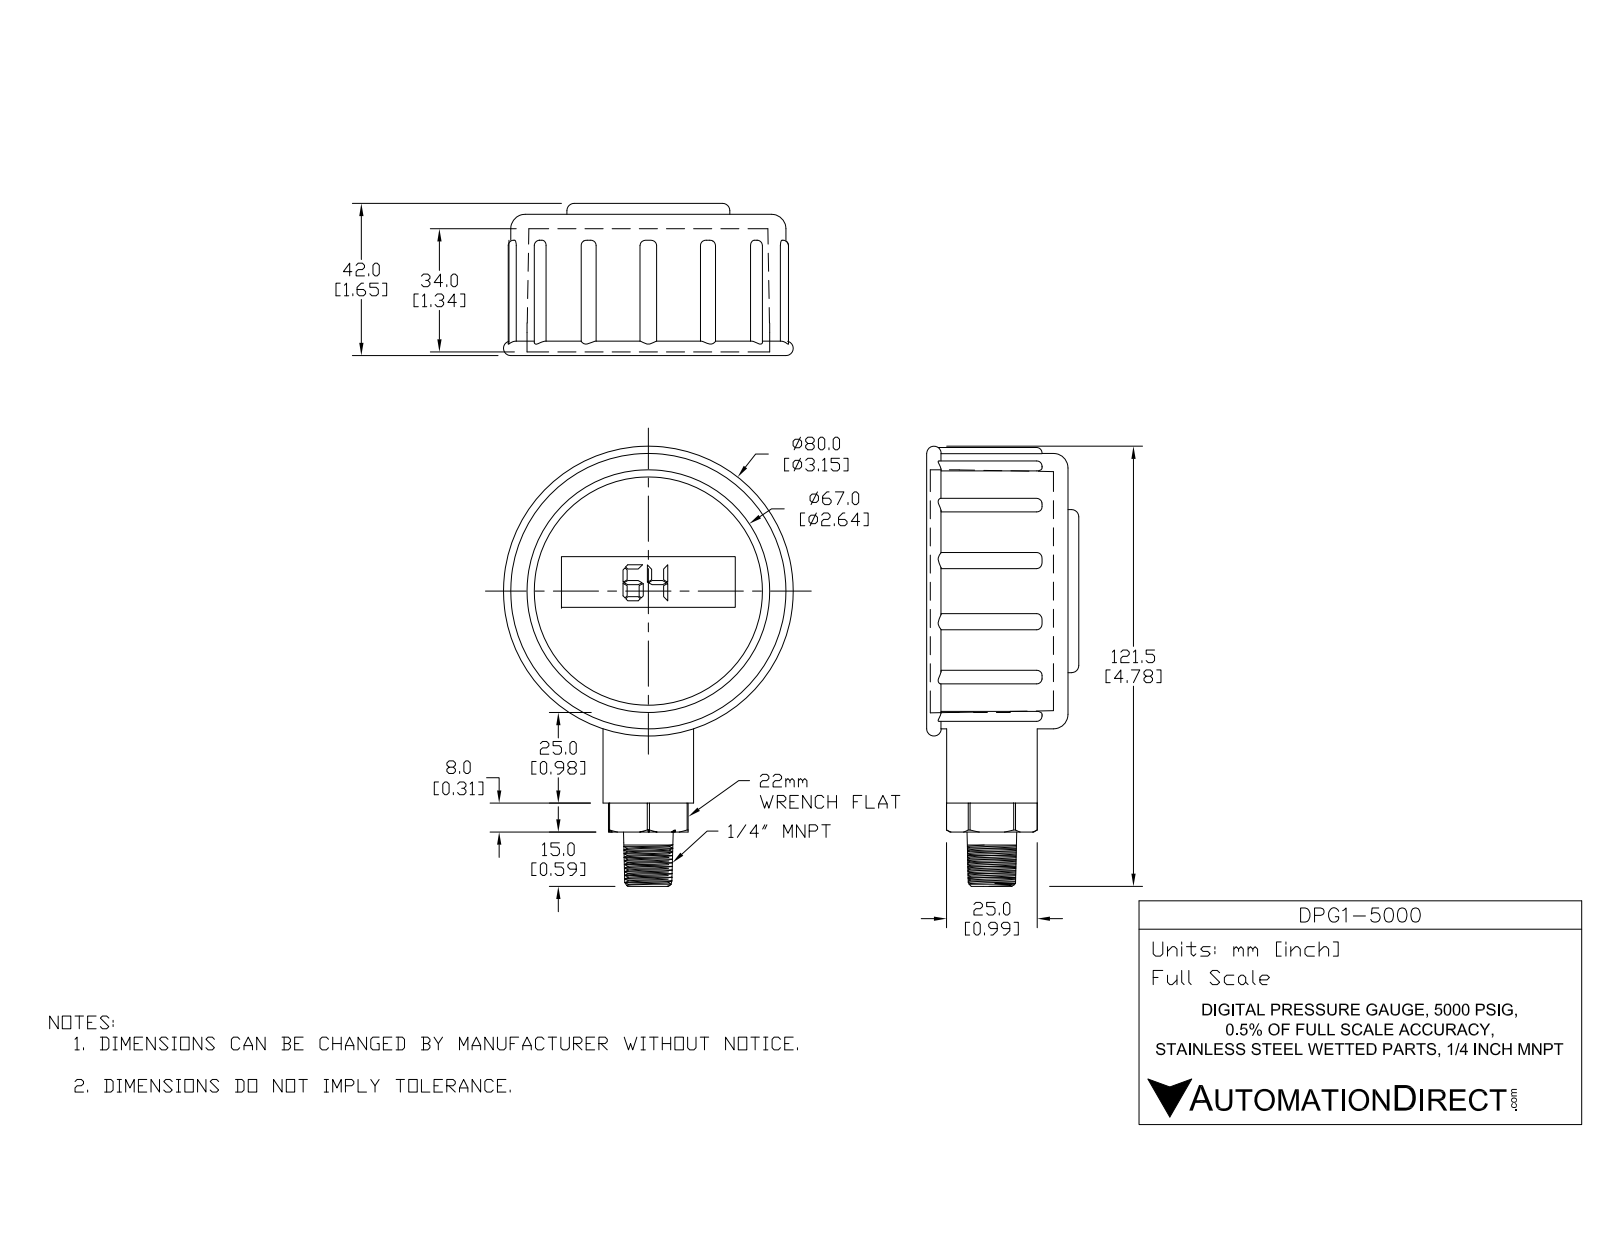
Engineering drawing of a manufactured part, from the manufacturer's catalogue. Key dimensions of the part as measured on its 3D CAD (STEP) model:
Part name (STEP PRODUCT): DPG1-5000
STEP written by: SolidWorks 2021 (CONFIG_CONTROL_DESIGN)
Units: millimetres
Bodies: 4 solids, 181 faces (71 planar, 49 cylindrical, 61 other)
Overall size (bounding box): 121.62 × 80 × 42
Volume: 196 180 mm³ · Surface area: 45 978 mm²
Round holes (diameter × count): ⌀63 ×1, ⌀67.19 ×1
Round bosses / shafts (diameter × count): ⌀76 ×1, ⌀67 ×1, ⌀45 ×1, ⌀25 ×1, ⌀10 ×1
Partial cylindrical surfaces — rounded edges, fillets, slot ends (radius × count): R2.38 ×13, R8.5 ×6, R38 ×1
Main face-to-face distances: 33.95, 4, 37.95, 3, 7, 40.95, 42, 39, 35, 1.05
